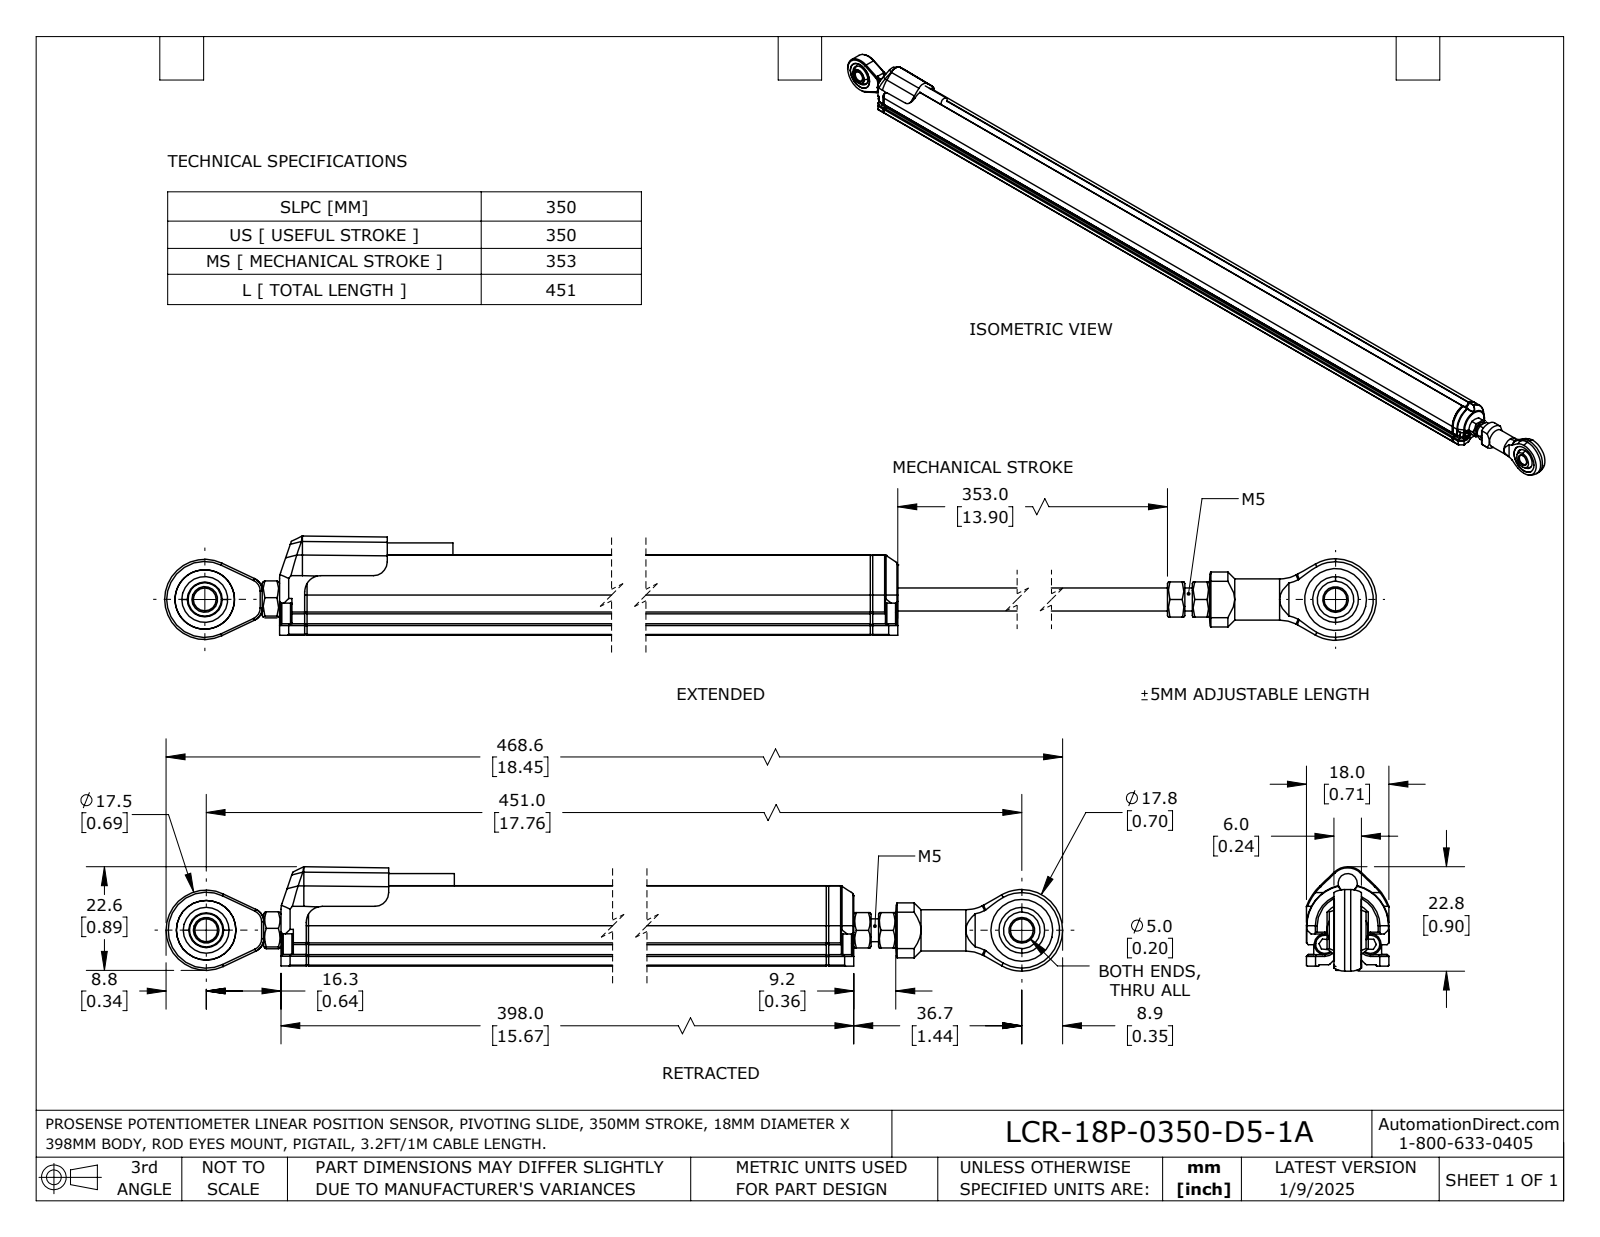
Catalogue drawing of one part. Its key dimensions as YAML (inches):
part_name: "LCR-18P-0350-D5-1A"
step_written_by: "SolidWorks 2023 (AUTOMOTIVE_DESIGN)"
units: inches
bodies: {solids: 20, faces: 515, planar: 289, cylindrical: 136, other: 90}
overall_size: [18.451, 0.896, 0.709]
volume: 6.723
surface_area: 61.99
round_holes:
  - {diameter: 0.197, count: 4}
  - {diameter: 0.102, count: 2}
  - {diameter: 0.104, count: 2}
  - {diameter: 0.394, count: 2}
  - {diameter: 0.213, count: 1}
  - {diameter: 0.272, count: 1}
  - {diameter: 0.512, count: 1}
  - {diameter: 0.531, count: 1}
round_bosses_or_shafts:
  - {diameter: 0.181, count: 4}
  - {diameter: 0.113, count: 3}
  - {diameter: 0.059, count: 2}
  - {diameter: 0.354, count: 1}
  - {diameter: 0.165, count: 1}
  - {diameter: 0.113, count: 1}
partial_cylinders:
  - {radius: 0.008, count: 12}
  - {radius: 0.004, count: 10}
  - {radius: 0.02, count: 8}
  - {radius: 0.012, count: 6}
  - {radius: 0.018, count: 6}
  - {radius: 0.016, count: 4}
  - {radius: 0.039, count: 4}
  - {radius: 0.043, count: 4}
face_to_face_distances: [0.709, 0.063, 0.646, 0.071, 0.059, 0.087, 0.098, 0.02, 0.028, 0.184]
hole_center_spacings: [0.231, 0.394, 0.23, 0.231, 17.756]
